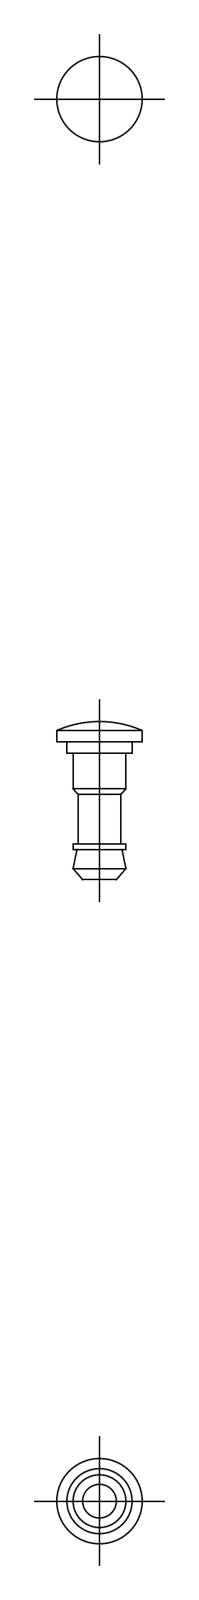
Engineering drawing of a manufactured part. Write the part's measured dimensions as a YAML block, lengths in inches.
part_name: "plunger"
step_written_by: "CADfix (AUTOMOTIVE_DESIGN)"
units: inches
bodies: {solids: 1, faces: 22, planar: 0, cylindrical: 0, other: 22}
overall_size: [0.555, 0.299, 0.299]
volume: 0.015
surface_area: 0.451
